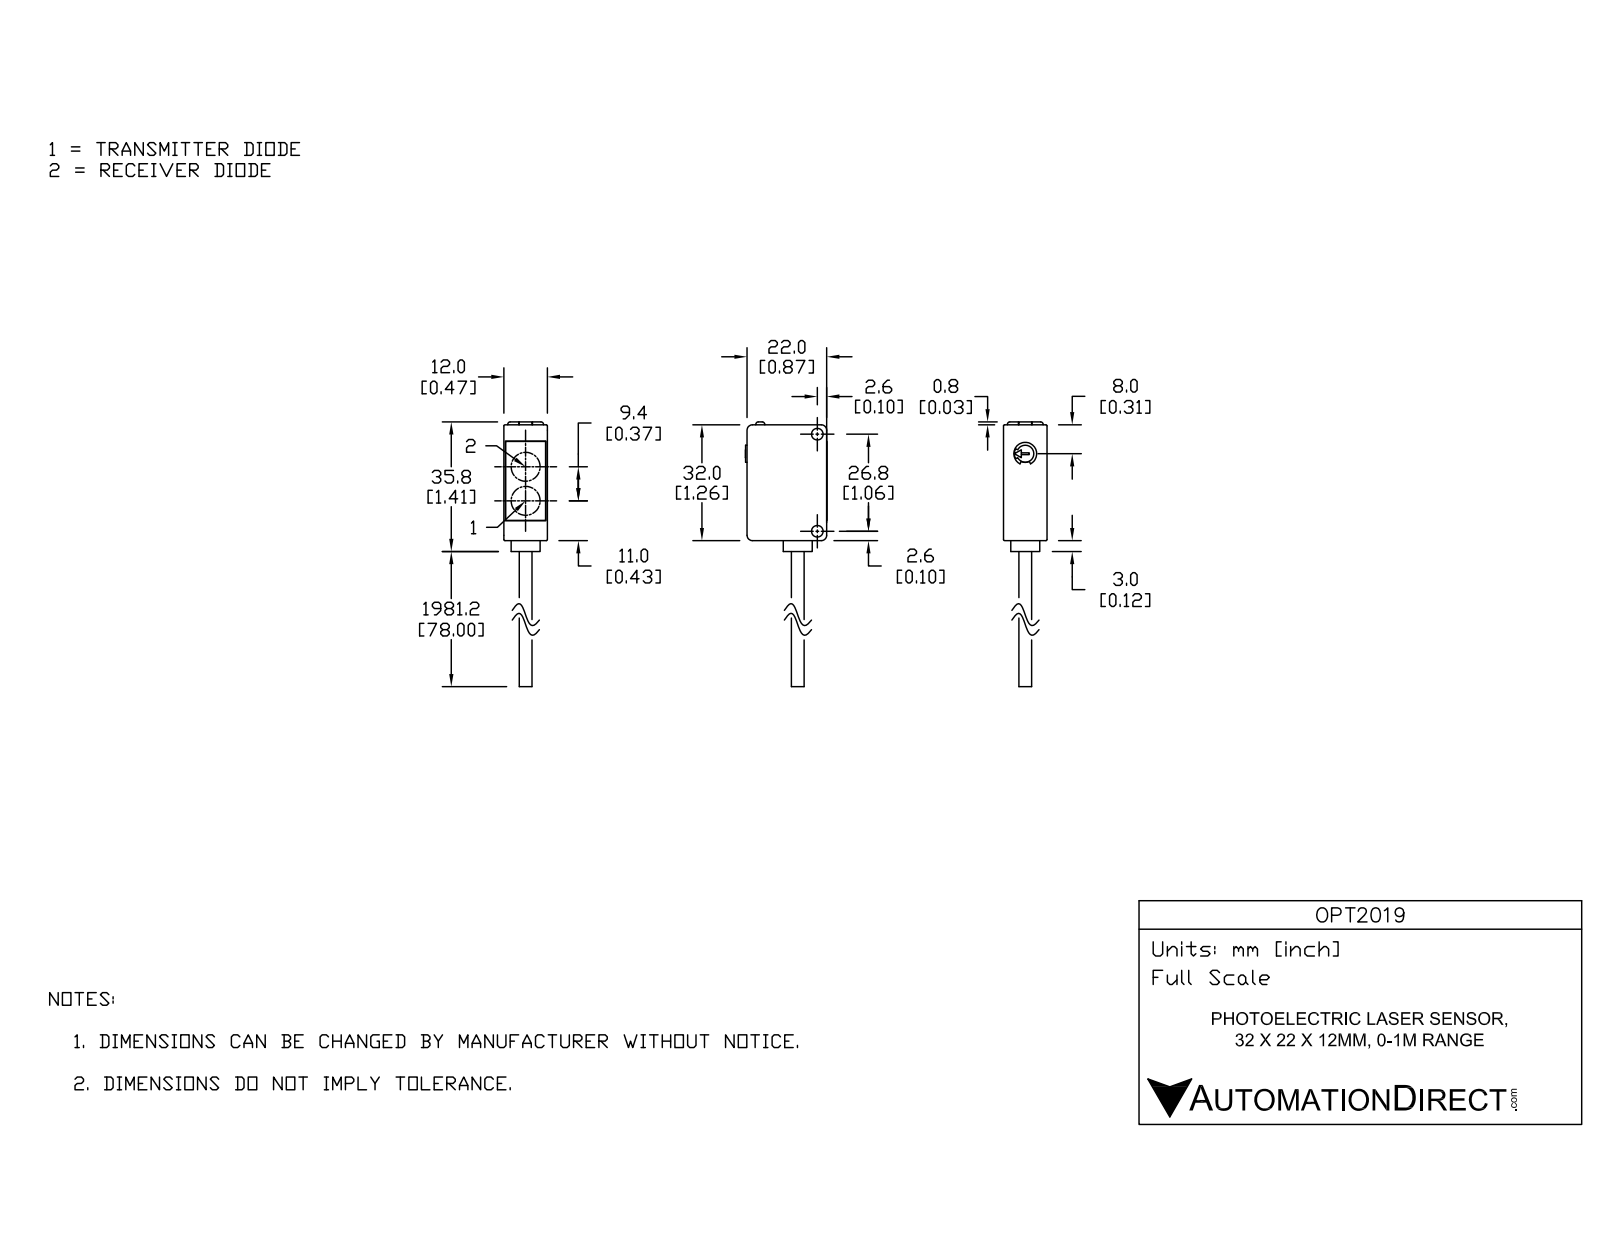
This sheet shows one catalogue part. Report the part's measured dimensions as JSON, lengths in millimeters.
{"part_name": "Füllkörper", "step_written_by": "Unknown (AUTOMOTIVE_DESIGN)", "units": "millimeters", "bodies": {"solids": 2, "faces": 155, "planar": 85, "cylindrical": 53, "other": 17}, "overall_size": [71.06, 22.5, 12], "volume_mm3": 8726, "surface_area_mm2": 3618, "round_holes": [[3.2, 2], [6.3, 1]], "round_bosses_or_shafts": [[8, 1], [4.7, 1], [3.5, 1]], "partial_cylinders_radius": [[0.3, 8], [0.5, 4], [1.5, 4], [0.1, 2], [0.7, 2], [1.25, 2], [1.9, 1], [2.4, 1]], "face_to_face_distances": [12, 22.1, 32, 22, 0.4, 0.5, 11.5, 11.6, 11.1, 3], "hole_center_spacings": [26.8]}
